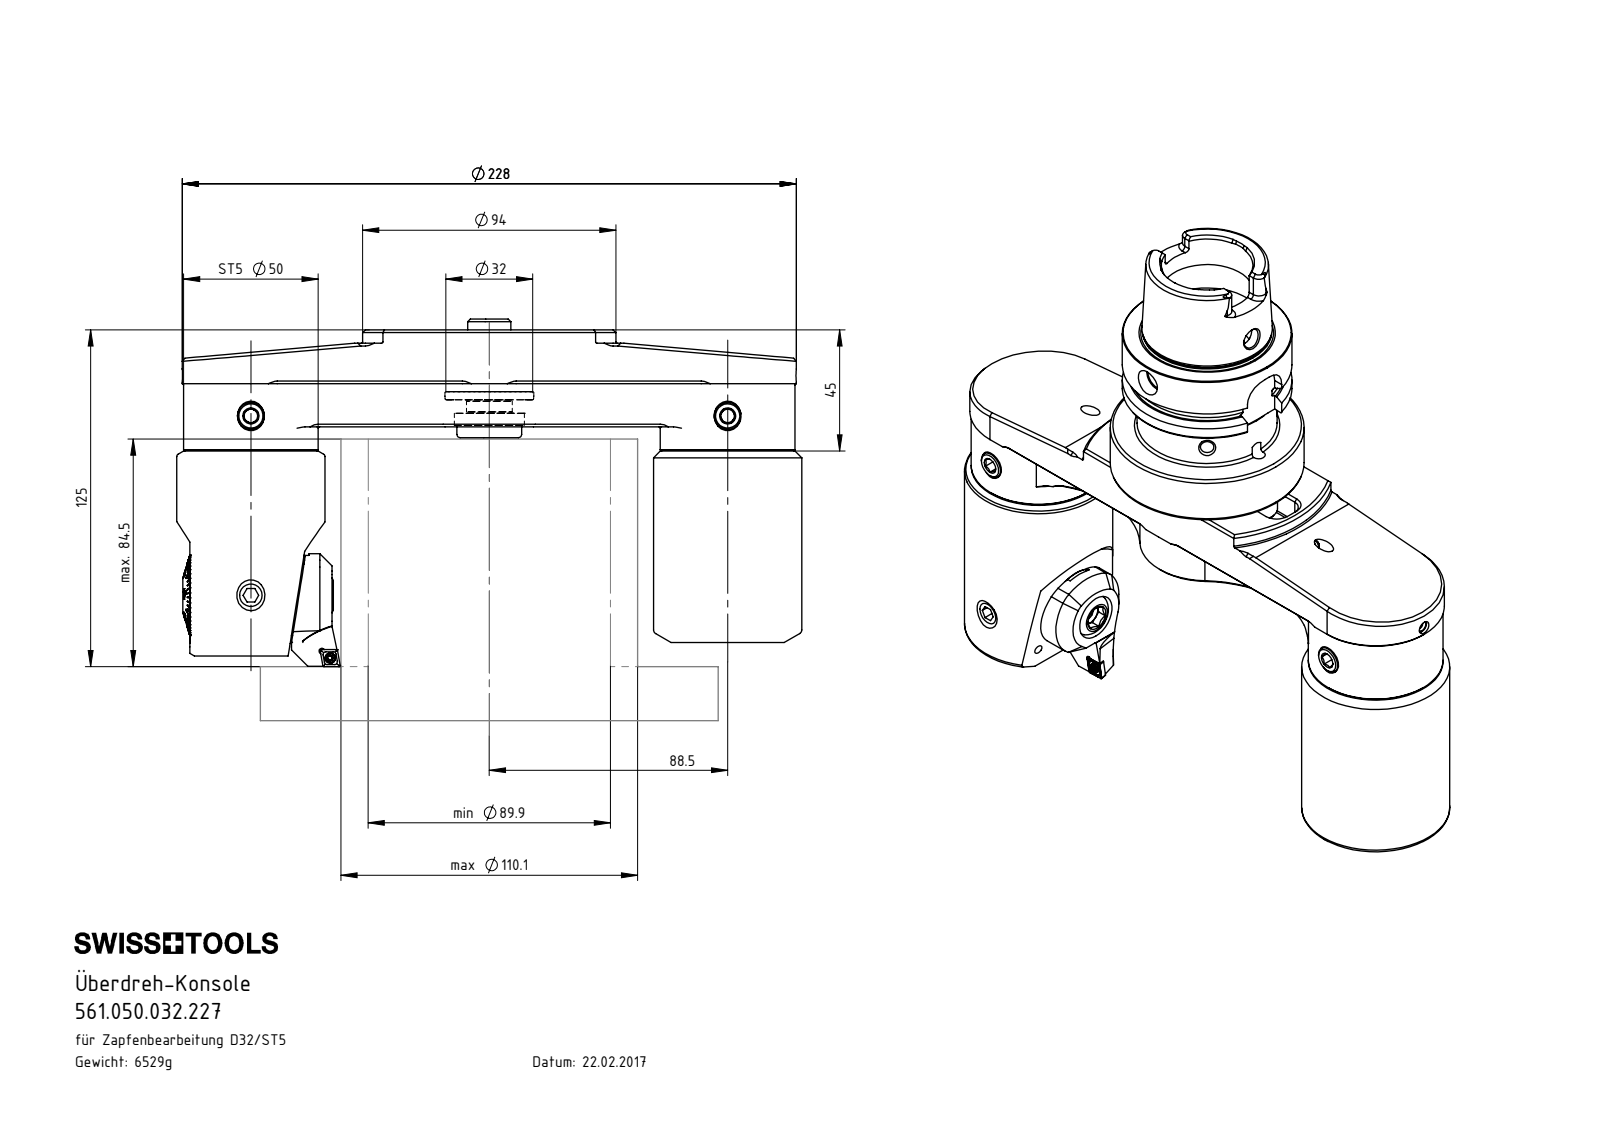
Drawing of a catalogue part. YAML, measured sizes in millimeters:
part_name: "DIN 3771 - 25x1.5; DIN 7984 - M16 x 35; ST5-F55.K21.080_min mit WP Halter; F55-BG2.015.015_B (+8 more)"
step_written_by: "SolidWorks 2017 (CONFIG_CONTROL_DESIGN)"
units: millimeters
bodies: {solids: 36, faces: 1811, planar: 542, cylindrical: 442, other: 827}
overall_size: [232, 216.9, 72]
volume: 821704
surface_area: 168671
round_holes:
  - {diameter: 5, count: 12}
  - {diameter: 3.3, count: 7}
  - {diameter: 4, count: 7}
  - {diameter: 4.2, count: 6}
  - {diameter: 8, count: 3}
  - {diameter: 12, count: 3}
  - {diameter: 30, count: 3}
  - {diameter: 6.8, count: 2}
  - {diameter: 8.5, count: 2}
  - {diameter: 9, count: 2}
  - {diameter: 10, count: 2}
  - {diameter: 10.2, count: 2}
round_bosses_or_shafts:
  - {diameter: 10, count: 4}
  - {diameter: 5, count: 3}
  - {diameter: 55, count: 2}
  - {diameter: 50, count: 2}
  - {diameter: 27.8, count: 2}
  - {diameter: 27.3, count: 2}
  - {diameter: 16, count: 2}
  - {diameter: 14, count: 2}
partial_cylinders:
  - {radius: 0.5, count: 12}
  - {radius: 0.21, count: 6}
  - {radius: 0.34, count: 6}
  - {radius: 0.59, count: 6}
  - {radius: 1.4, count: 6}
  - {radius: 0.36, count: 5}
  - {radius: 2.88, count: 4}
  - {radius: 4.2, count: 4}
face_to_face_distances: [5, 45, 16, 9, 25, 20, 36, 10, 51, 80]
hole_center_spacings: [177, 16.9, 0.5, 12.25, 17.05, 20.28, 22.27, 27]
